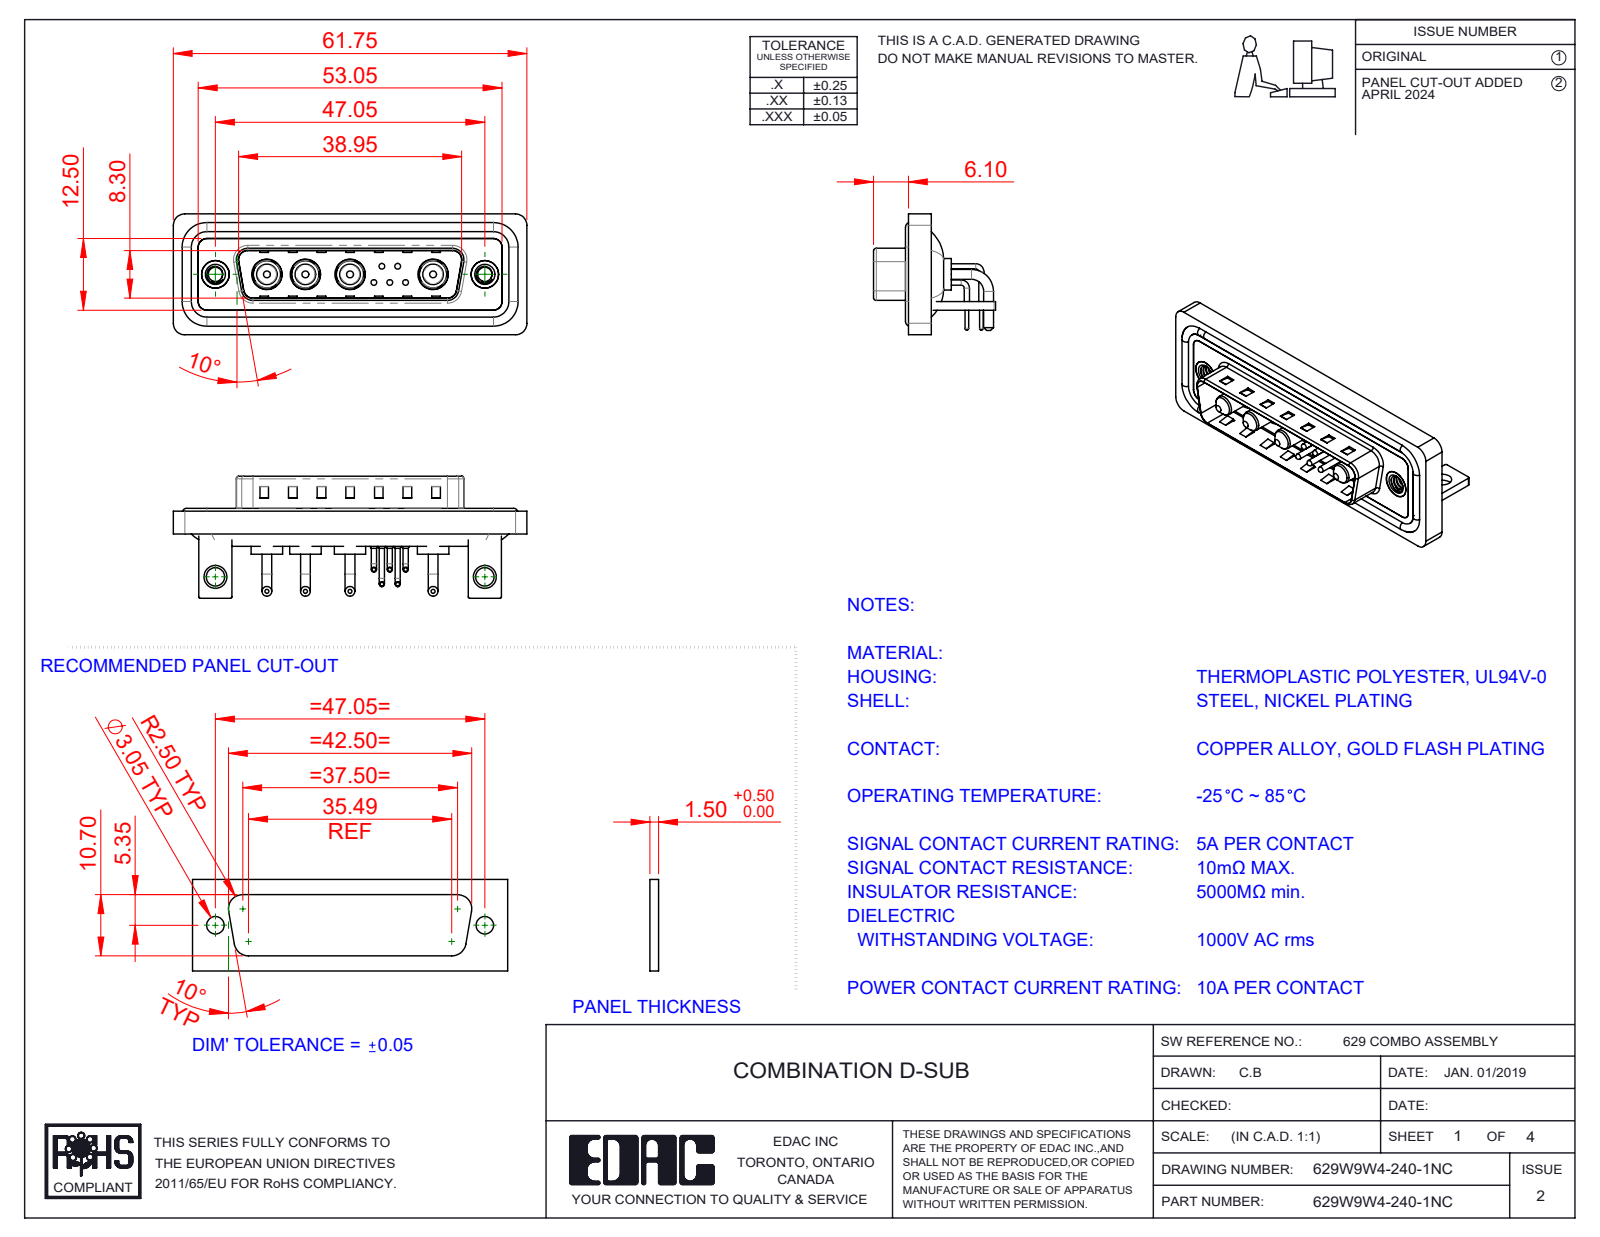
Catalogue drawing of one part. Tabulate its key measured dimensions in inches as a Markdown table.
| quantity | value |
| --- | --- |
| part name | 629Combo Contact Row 1; 629Combo Housing_9W4; 629Combo Shell Front_25 Contacts; 629Combo Shell Rear_25 Contacts (+6 more) |
| STEP written by | SolidWorks 2023 (CONFIG_CONTROL_DESIGN) |
| units | inches |
| bodies | 22 solids, 1243 faces (589 planar, 470 cylindrical, 184 other) |
| overall size | 2.431 × 0.839 × 0.831 |
| volume | 0.473 in³ |
| surface area | 19.78 in² |
| round holes (diameter × count) | 0.03 × 5, 0.063 × 5, 0.079 × 5, 0.191 × 4, 0.209 × 4, 0.098 × 2, 0.126 × 2, 0.157 × 2, 0.189 × 2, 0.197 × 2 |
| round bosses / shafts (diameter × count) | 0.035 × 10, 0.067 × 8, 0.059 × 5, 0.039 × 5, 0.026 × 5, 0.217 × 4, 0.205 × 4, 0.187 × 4 |
| partial cylindrical surfaces (radius × count) | 0.079 × 19, 0.059 × 18, 0.01 × 16, 0.02 × 9, 0.063 × 8, 0.04 × 5, 0.024 × 4, 0.026 × 4 |
| main face-to-face distances | 0.016, 0.059, 0.031, 0.114, 0.083, 0.043, 0.146, 0.161, 0.177, 0.063 |
| hole center spacings | 0.124, 0.109, 0.198, 0.571, 1.852, 0.109, 0.173, 0.174 |
